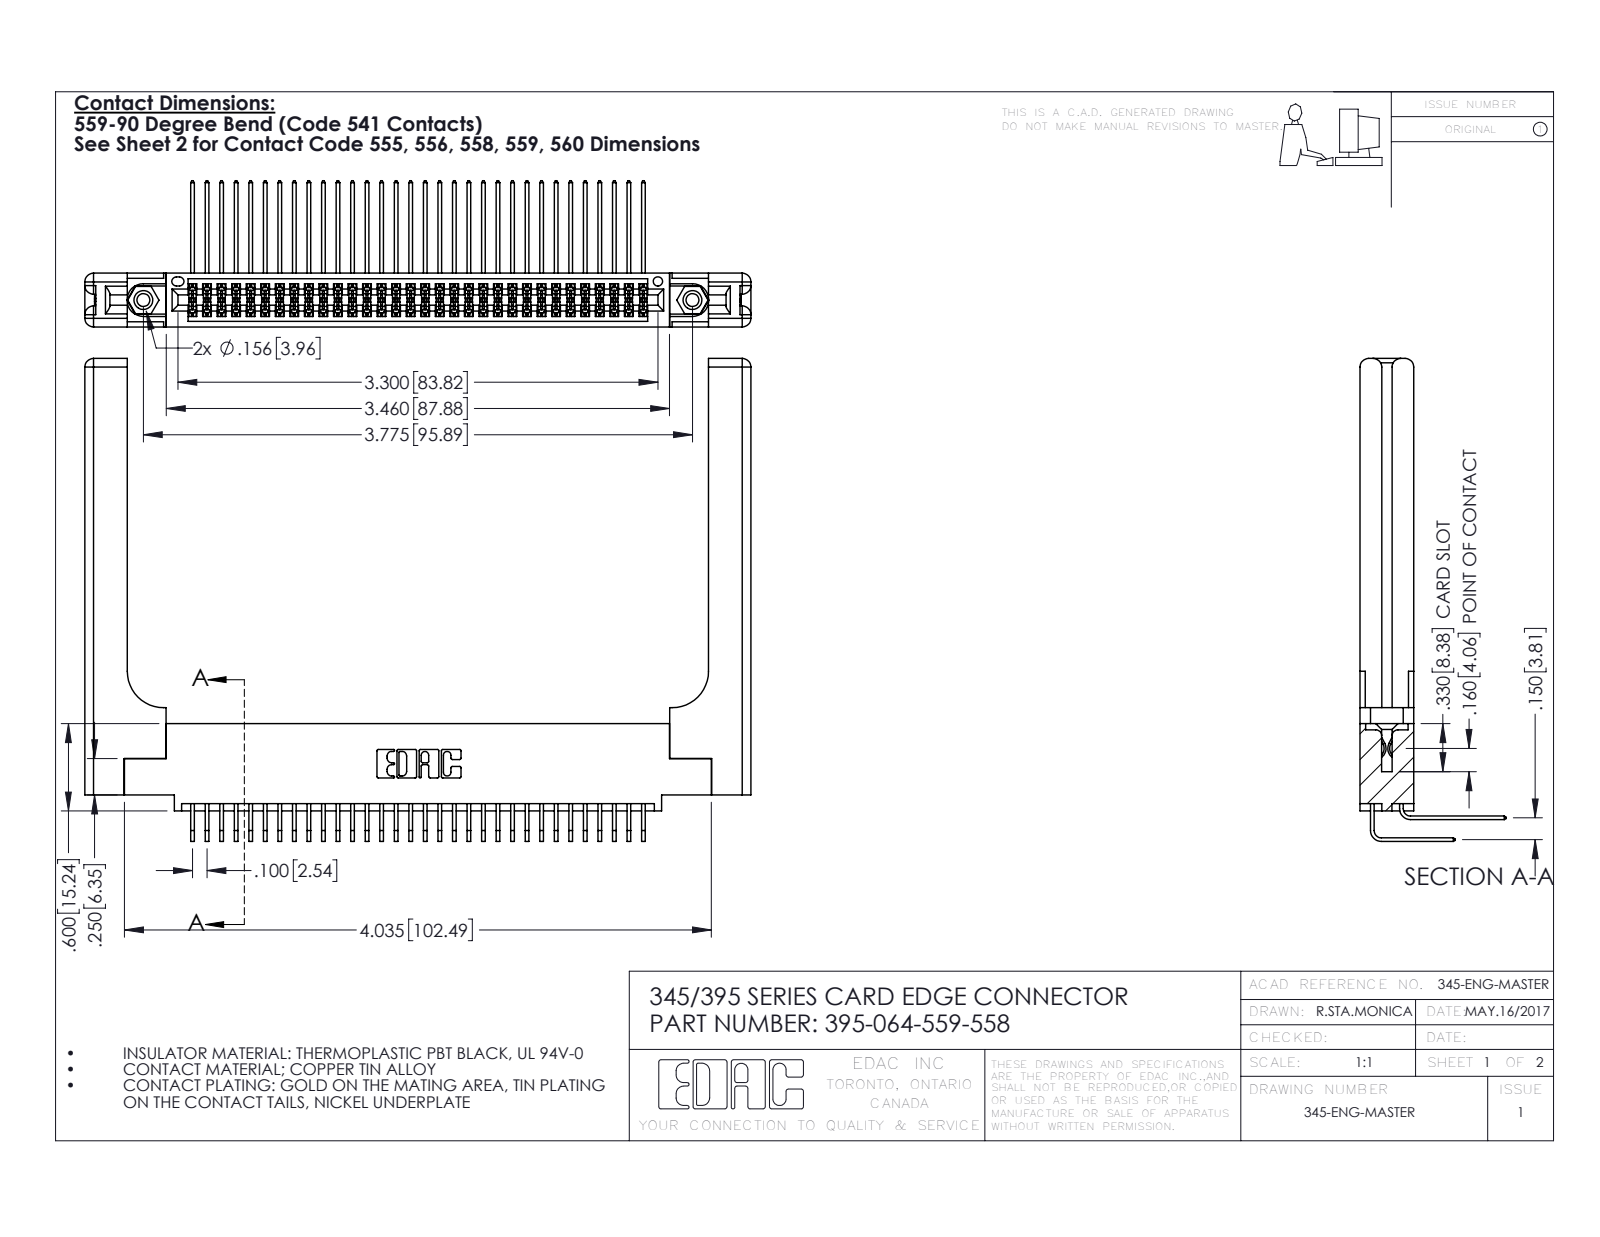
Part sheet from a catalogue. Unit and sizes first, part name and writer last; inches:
Units: inches
Overall size (bounding box): 4.579 × 3.319 × 1.005
Round holes (diameter × count): ⌀0.089 ×2, ⌀0.125 ×2, ⌀0.156 ×2, ⌀0.064 ×1
Round bosses / shafts (diameter × count): ⌀0.155 ×2
Partial cylindrical surfaces — rounded edges, fillets, slot ends (radius × count): R0.006 ×96, R0.01 ×22, R0.06 ×16, R0.007 ×6, R0.031 ×6, R0.026 ×3, R0.014 ×2, R0.019 ×2
Main face-to-face distances: 0.072, 0.37, 0.298, 0.098, 0.272, 0.025, 0.2, 0.225, 0.148, 0.15
Hole centre spacings: 0.27, 3.54, 3.775
Volume: 1.219 in³ · Surface area: 36.73 in²
Bodies: 69 solids, 3714 faces (2472 planar, 1182 cylindrical, 60 other)
Part name (STEP PRODUCT): 345-292-001_559 Tail - 2; 345-292-001_558 559 Tail - 1; 345-220-058_345-220-058; 345 Part_0.110 Offset - 0.156 Dia-TH (+2 more)
STEP written by: SolidWorks 2016 (CONFIG_CONTROL_DESIGN)
